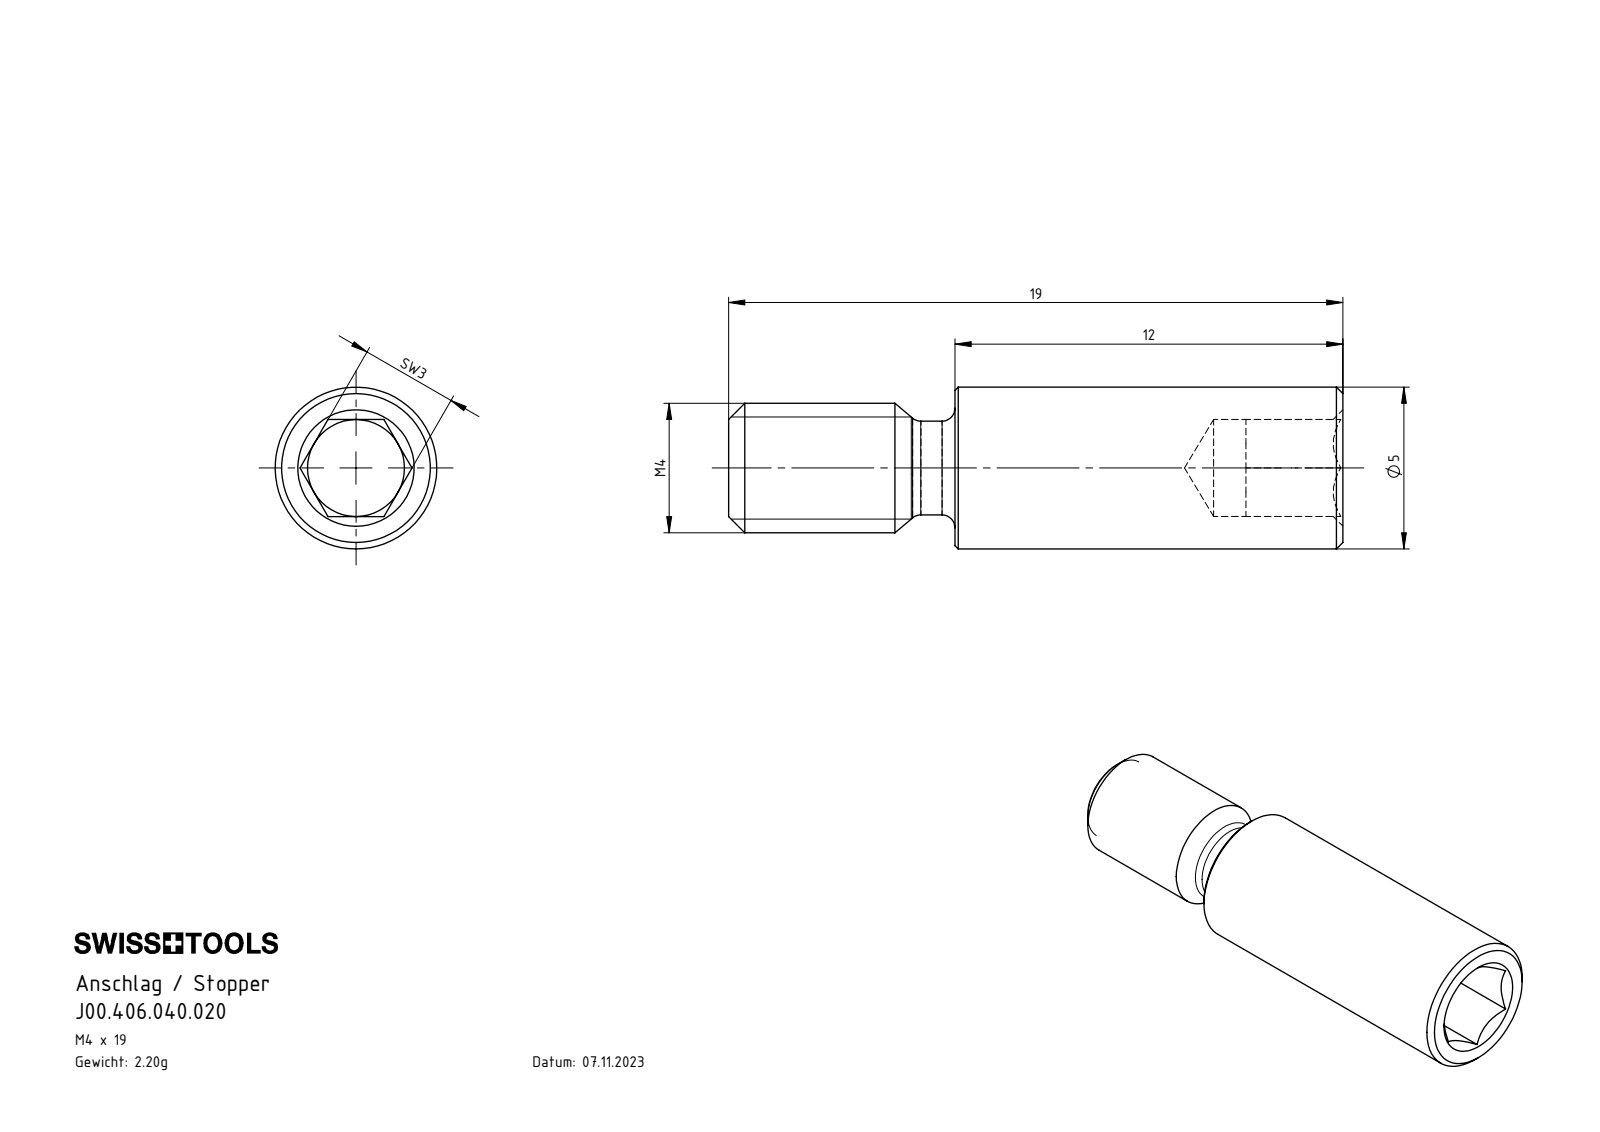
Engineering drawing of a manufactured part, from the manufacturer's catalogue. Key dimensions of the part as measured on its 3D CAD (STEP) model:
Part name (STEP PRODUCT): J00.406.040.020
STEP written by: SolidWorks 2022 (AUTOMOTIVE_DESIGN)
Units: millimetres
Bodies: 1 solid, 39 faces (15 planar, 8 cylindrical, 16 other)
Overall size (bounding box): 19 × 5 × 5
Volume: 280 mm³ · Surface area: 351 mm²
Round holes (diameter × count): ⌀3 ×1
Round bosses / shafts (diameter × count): ⌀5 ×1, ⌀4 ×1, ⌀2.9 ×1
Main face-to-face distances: 3, 7, 19, 12, 16, 9
